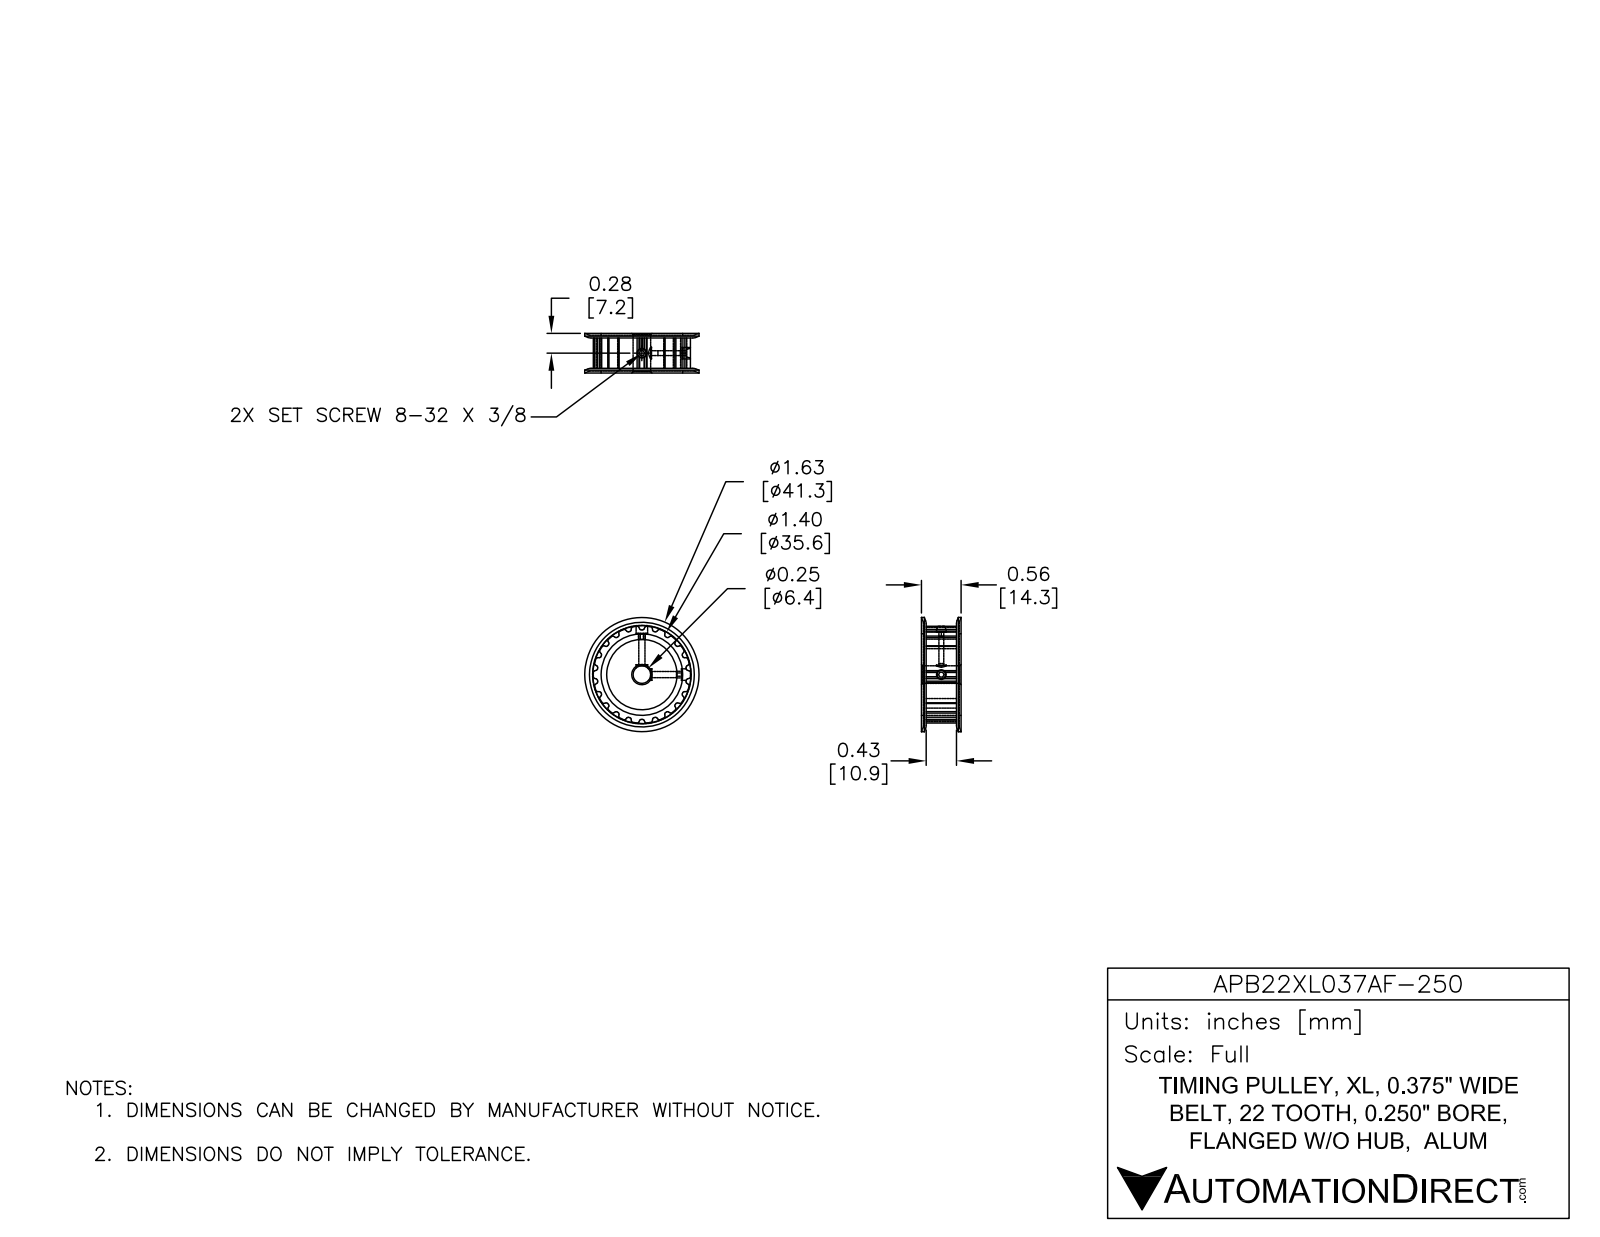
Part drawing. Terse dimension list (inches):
name: APB22XL037AF-250
written by: SolidWorks 2014 (AUTOMOTIVE_DESIGN)
unit: in
bodies: 1 solid, 231 faces (77 planar, 142 cylindrical, 12 other)
size: 1.625 × 1.625 × 0.56
volume: 0.717 in³; area: 8.958 in²
holes: 2× ⌀0.089, 2× ⌀0.125, 1× ⌀0.25
bosses: 1× ⌀0.5
rounds: 88× R0.015, 1× R0.636
face distances: 0.495, 0.033, 0.032, 1.381, 0.065, 0.491, 0.527, 0.528, 0.56, 0.462
